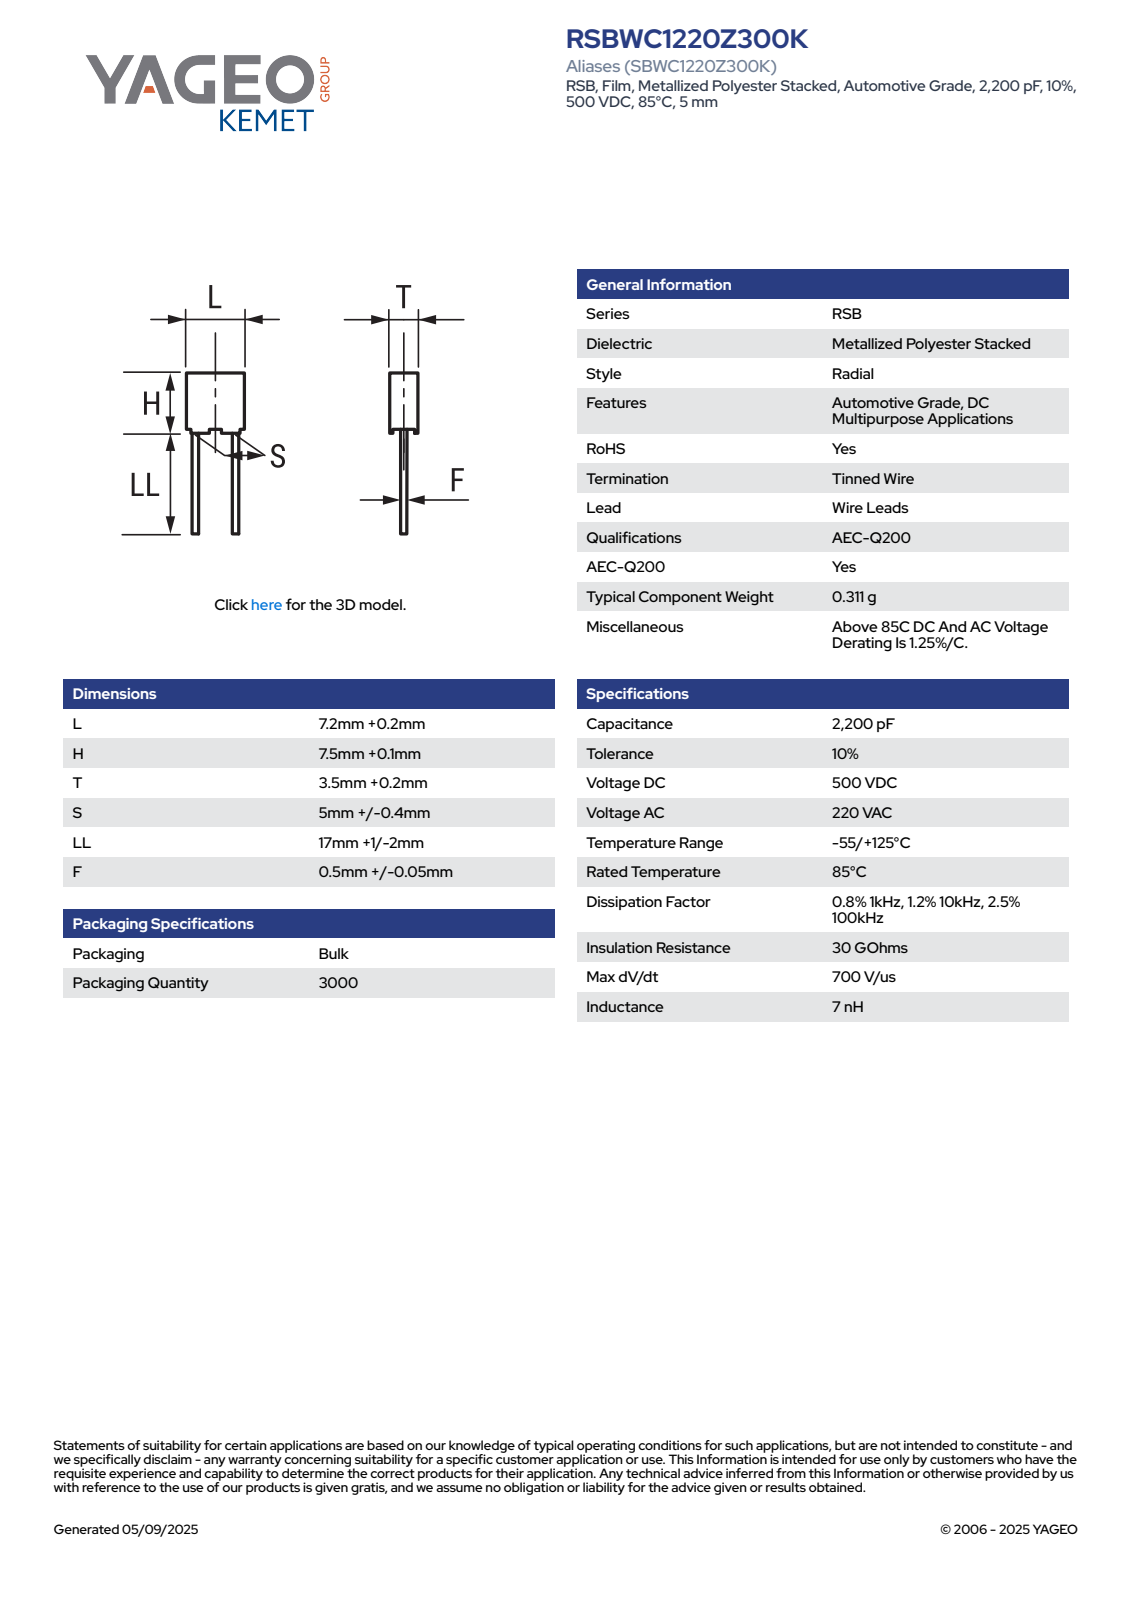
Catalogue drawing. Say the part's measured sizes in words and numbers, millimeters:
The part is named "CFR_RB3_7.2X7.5X3.5_L7.4H7.6T3.7S5LL18F0.65". Its 3-D file was written by "SolidWorks 2014 (AUTOMOTIVE_DESIGN)". It is 4 solids with 85 faces: 77 planar, 8 cylindrical and 0 other. Overall it measures 25.6 by 7.4 by 3.71 millimeters. Its volume is 203 cubic millimeters and its surface area 313 square millimeters. Round bosses or shafts: 2 of diameter 0.65. Partial cylindrical surfaces (rounded edges, fillets, slot ends): 4 of radius 0.5. The main face-to-face distances are 3.7, 7.4, 6.85, 3.45, 7.15, 3.2, 0.75, 7.6, 6.9, 3.71.
